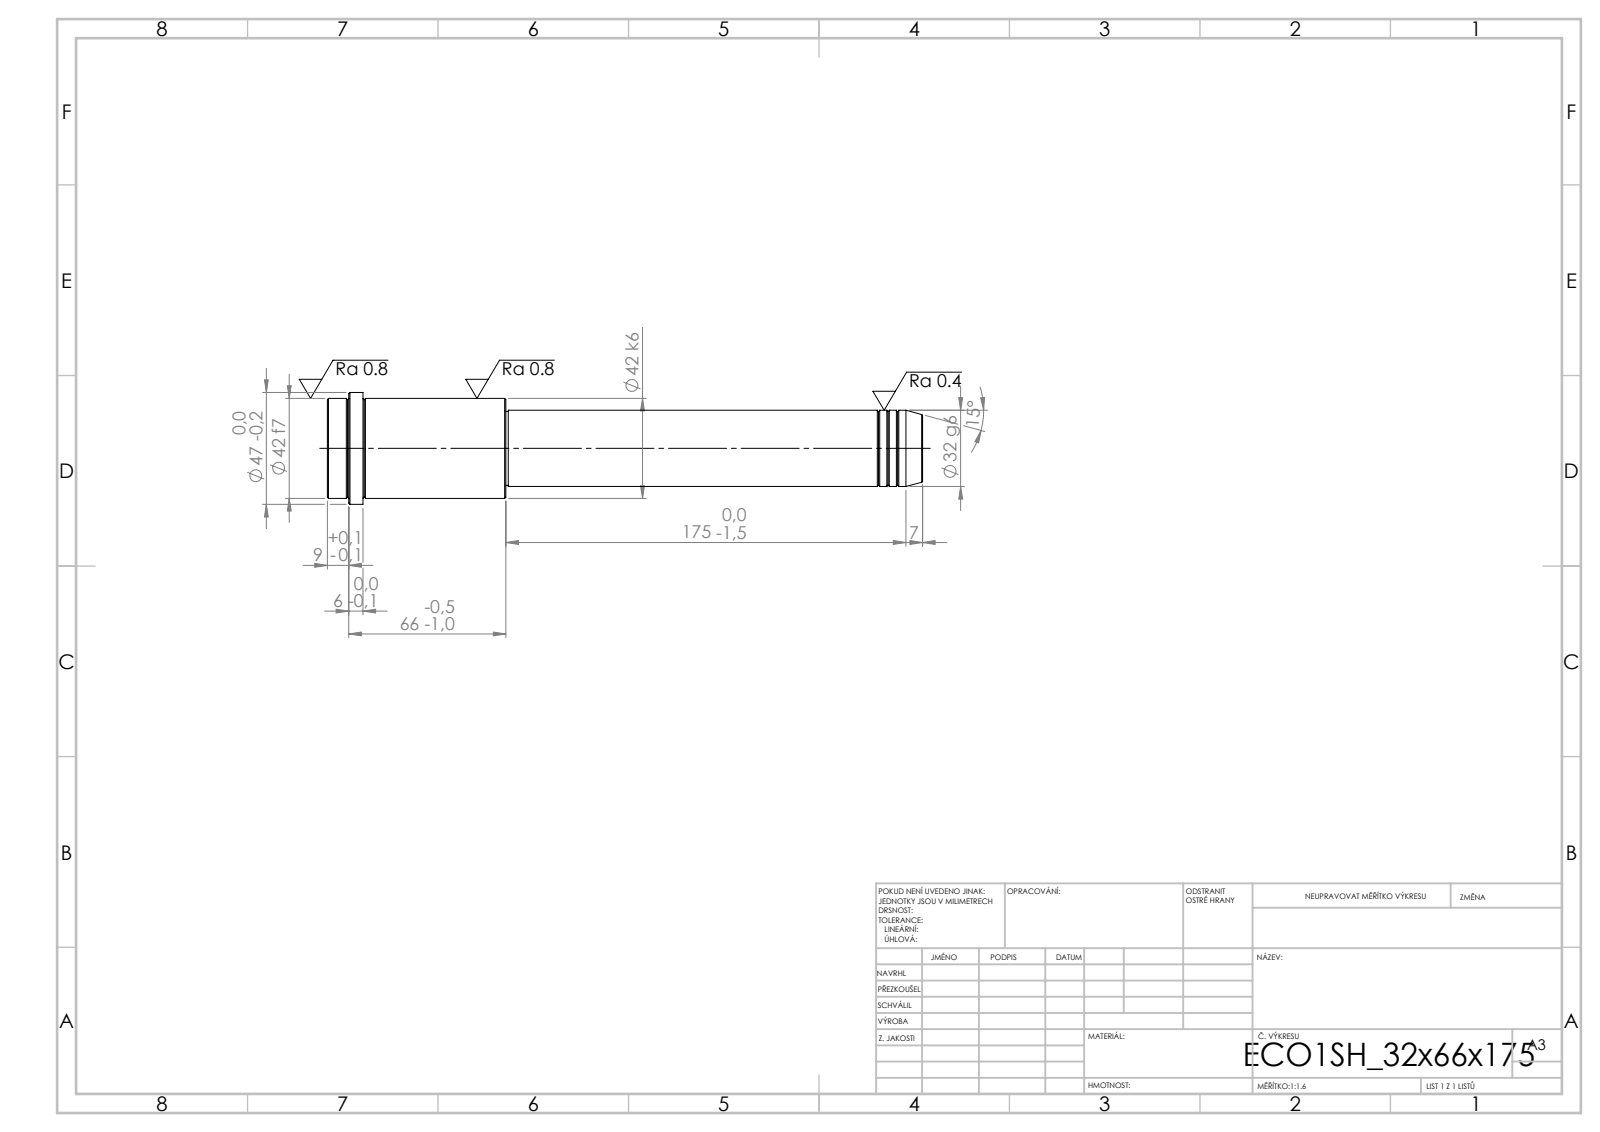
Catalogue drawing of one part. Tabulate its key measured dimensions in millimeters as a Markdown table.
| quantity | value |
| --- | --- |
| STEP written by | SolidWorks 2019 (CONFIG_CONTROL_DESIGN) |
| units | millimeters |
| bodies | 1 solid, 52 faces (6 planar, 16 cylindrical, 30 other) |
| overall size | 250 × 47 × 47 |
| volume | 245 792 mm³ |
| surface area | 31 129 mm² |
| round bosses / shafts (diameter × count) | 47 × 1, 42 × 1, 32 × 1, 31 × 1 |
| main face-to-face distances | 250, 175, 75, 235, 60, 15, 241, 66, 6, 9 |
